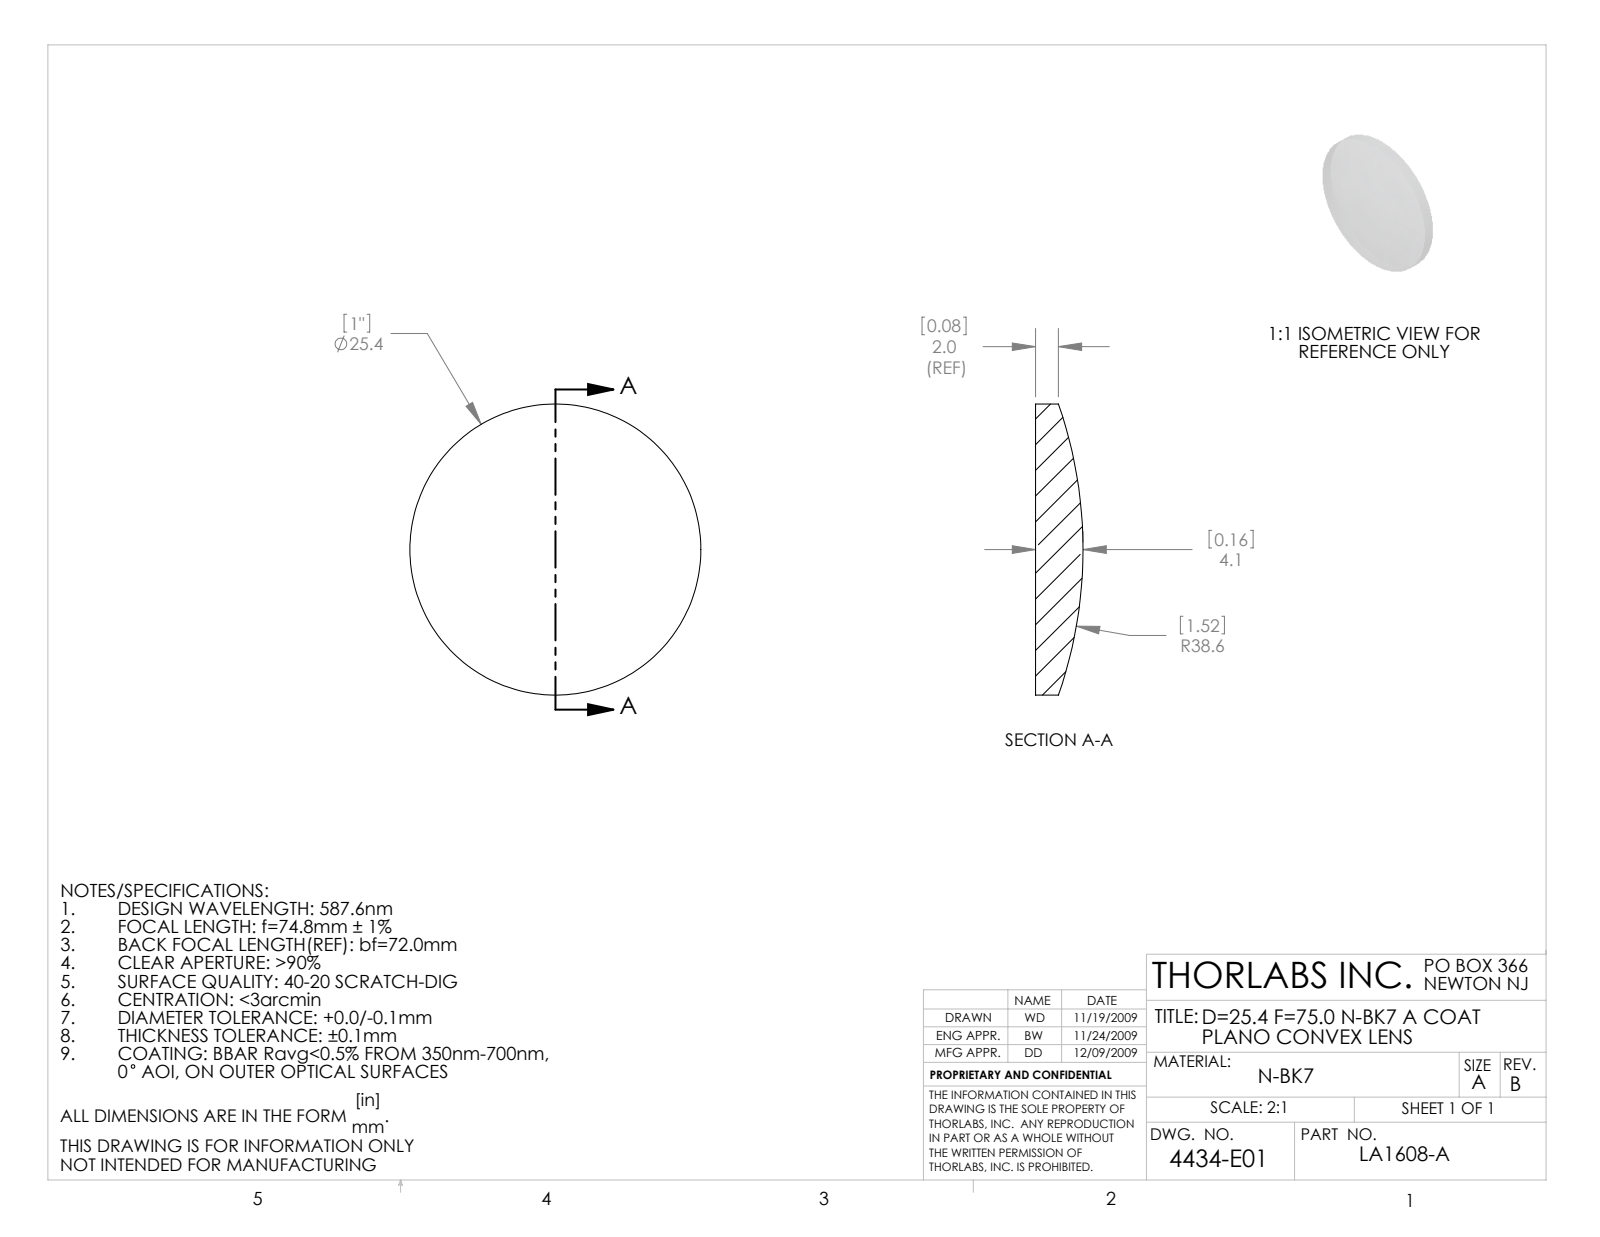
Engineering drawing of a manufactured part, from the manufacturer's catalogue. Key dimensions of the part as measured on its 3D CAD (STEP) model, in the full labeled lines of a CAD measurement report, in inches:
Part name (STEP PRODUCT): 4434-E0W
STEP written by: SolidWorks 2009 (AUTOMOTIVE_DESIGN)
Units: inches
Bodies: 1 solid, 5 faces (1 planar, 2 cylindrical, 2 other)
Overall size (bounding box): 1 × 1 × 0.163
Volume: 0.095 in³ · Surface area: 1.84 in²
Round bosses / shafts (diameter × count): ⌀1 ×1
